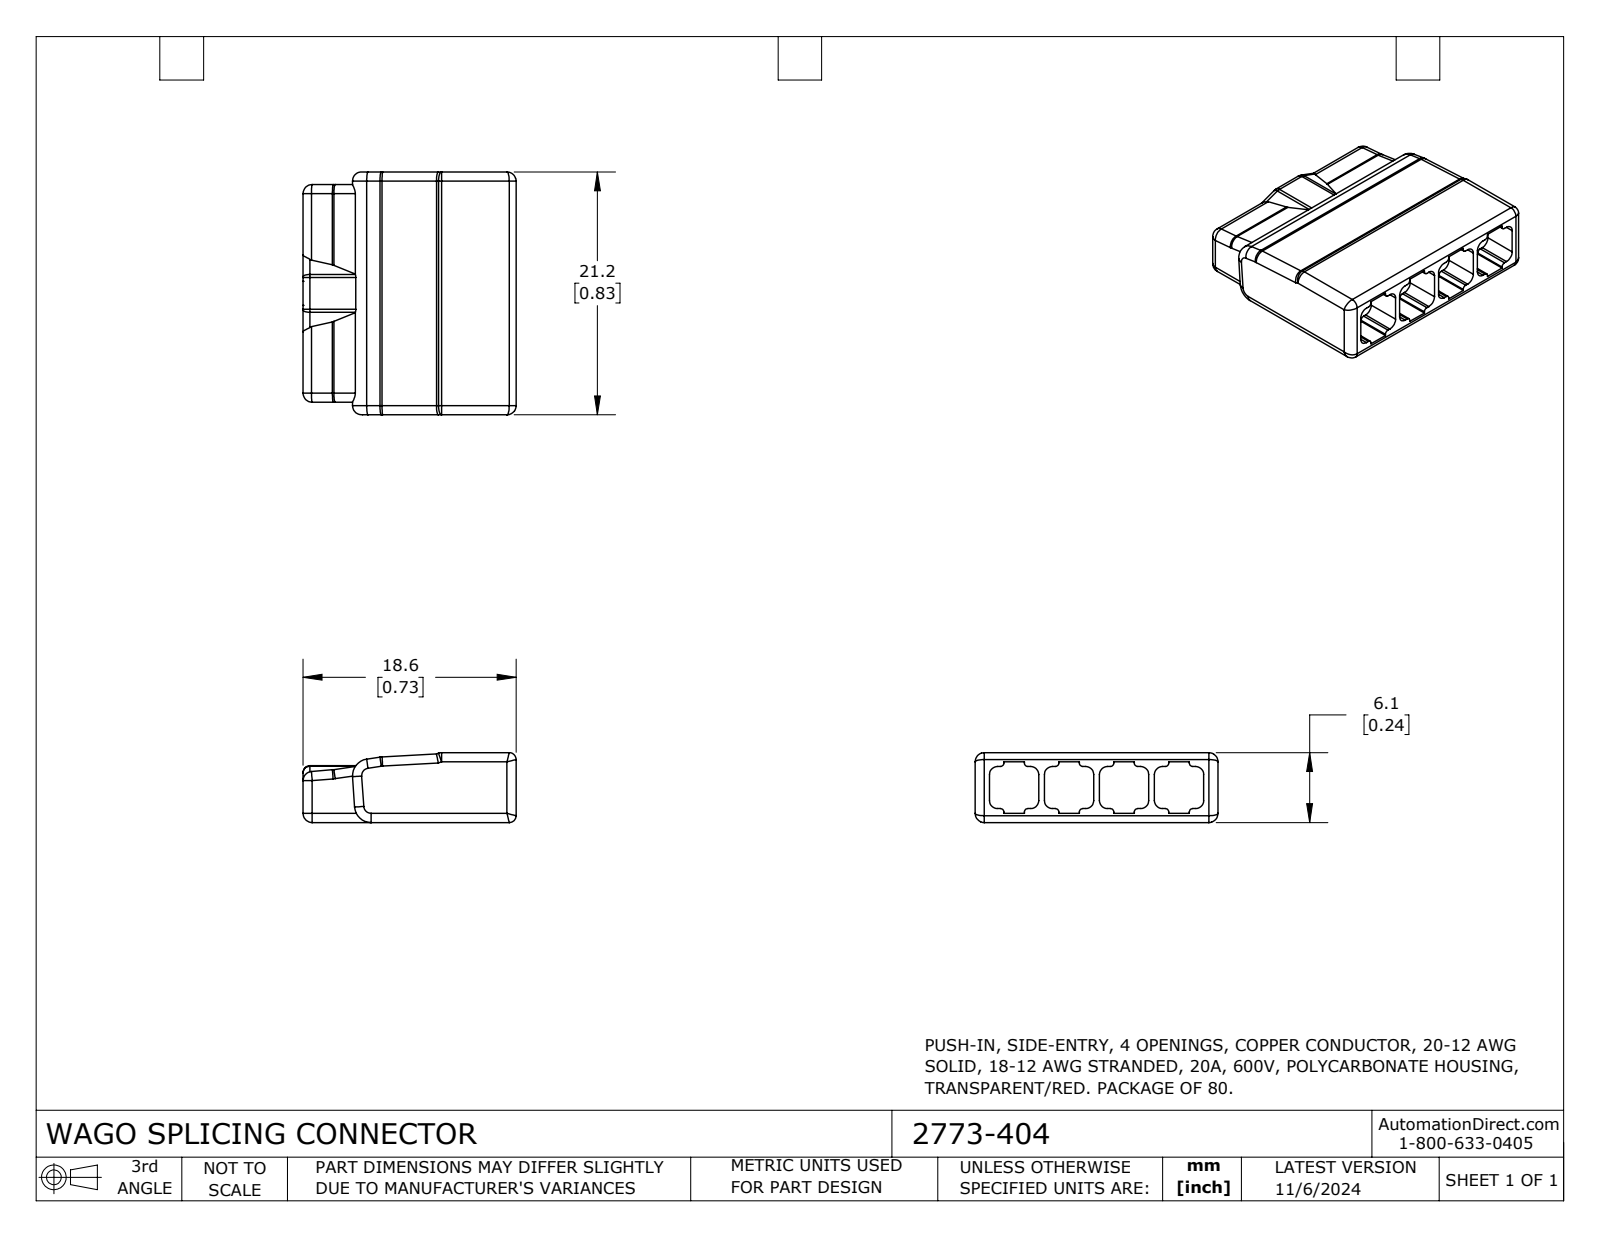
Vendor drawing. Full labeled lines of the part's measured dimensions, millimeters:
Part name (STEP PRODUCT): 2773-404
STEP written by: SolidWorks 2023 (CONFIG_CONTROL_DESIGN)
Units: millimetres
Bodies: 1 solid, 169 faces (78 planar, 71 cylindrical, 20 other)
Overall size (bounding box): 21.2 × 18.6 × 6.1
Volume: 1 927 mm³ · Surface area: 1 363 mm²
Partial cylindrical surfaces — rounded edges, fillets, slot ends (radius × count): R0.8 ×27, R0.3 ×16, R0.7 ×16, R0.6 ×5, R1.45 ×2, R2 ×2
Main face-to-face distances: 6.1, 21.2, 15.6, 4.8, 0.8, 5.3, 3, 9.6, 18.6, 4.3
